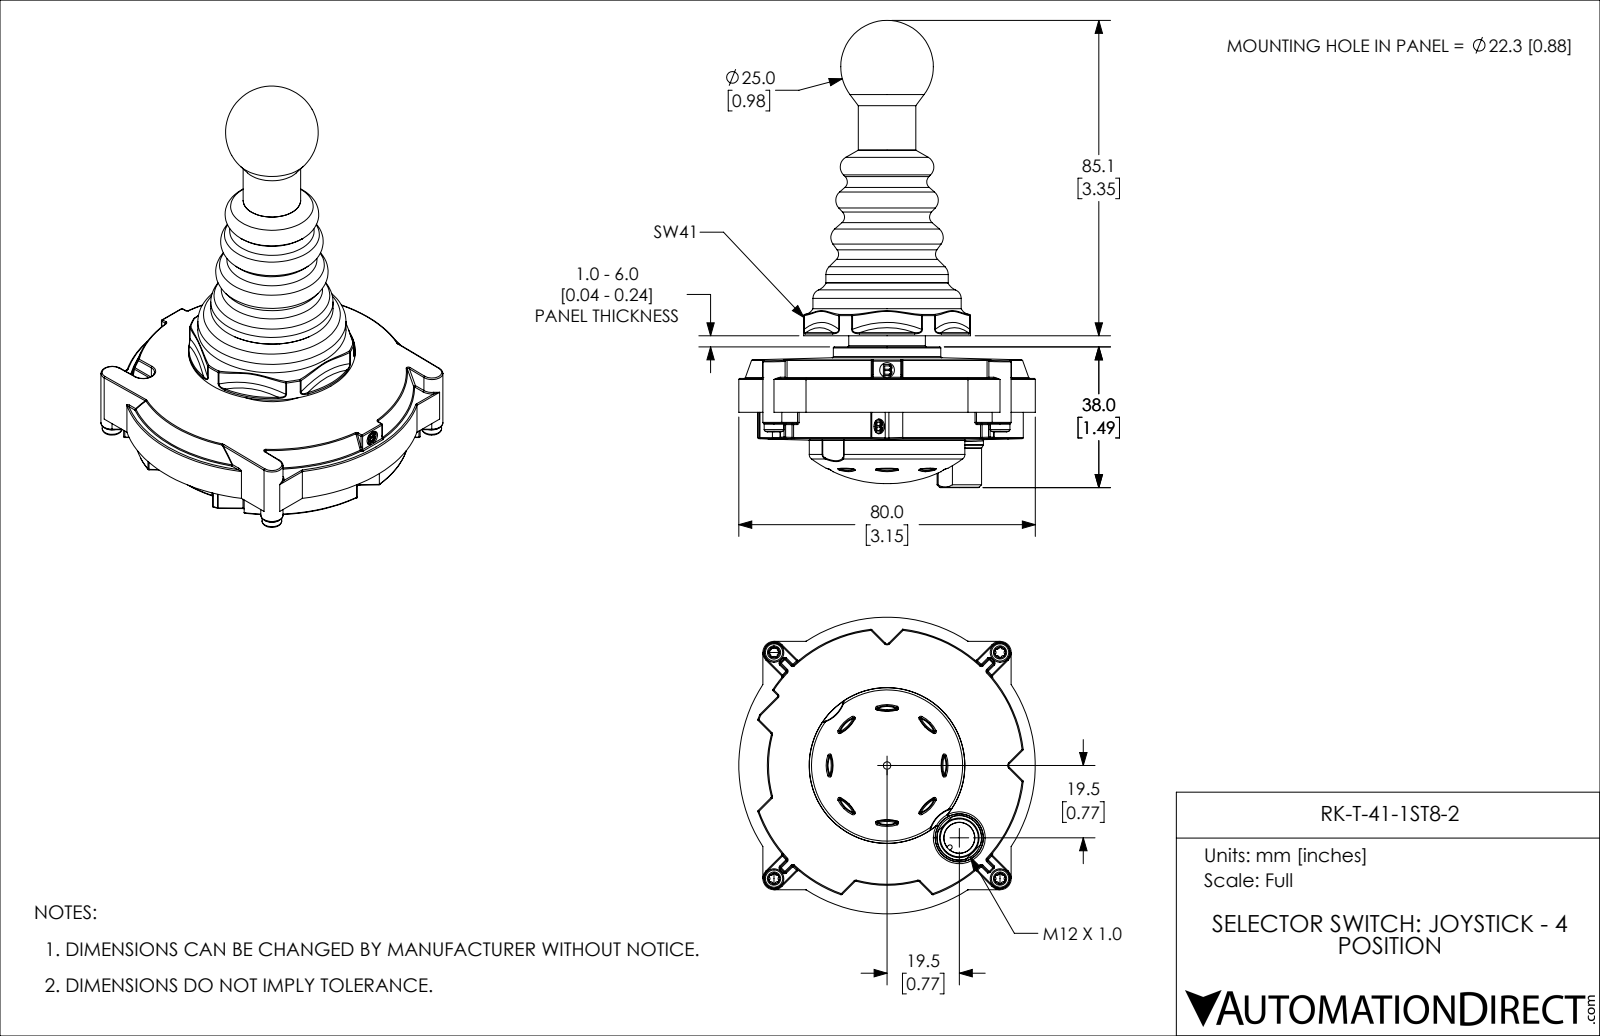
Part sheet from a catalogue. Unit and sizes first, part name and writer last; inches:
Units: inches
Overall size (bounding box): 4.961 × 3.15 × 3.15
Round holes (diameter × count): ⌀0.157 ×5, ⌀0.115 ×4, ⌀0.327 ×1, ⌀0.331 ×1, ⌀1.228 ×1, ⌀1.461 ×1, ⌀1.579 ×1
Round bosses / shafts (diameter × count): ⌀0.209 ×4, ⌀1.772 ×1, ⌀1.654 ×1, ⌀1.575 ×1, ⌀1.303 ×1, ⌀1.299 ×1, ⌀1.142 ×1, ⌀0.984 ×1
Partial cylindrical surfaces — rounded edges, fillets, slot ends (radius × count): R0.012 ×115, R0.007 ×44, R0.02 ×12, R0.102 ×8, R0.354 ×8, R0.024 ×7, R0.118 ×5, R0.027 ×2
Main face-to-face distances: 1.376, 0.555, 0.821, 2.638, 2.784, 1.963, 1.408, 1.016, 0.36, 0.461
Hole centre spacings: 2.402, 1.698, 0.177, 2.016, 2.224, 3.396, 0.613, 1.086
Volume: 10.1 in³ · Surface area: 50.22 in²
Bodies: 4 solids, 1358 faces (374 planar, 341 cylindrical, 643 other)
Part name (STEP PRODUCT): RK-T-41-1ST8-2
STEP written by: SolidWorks 2019 (CONFIG_CONTROL_DESIGN)
